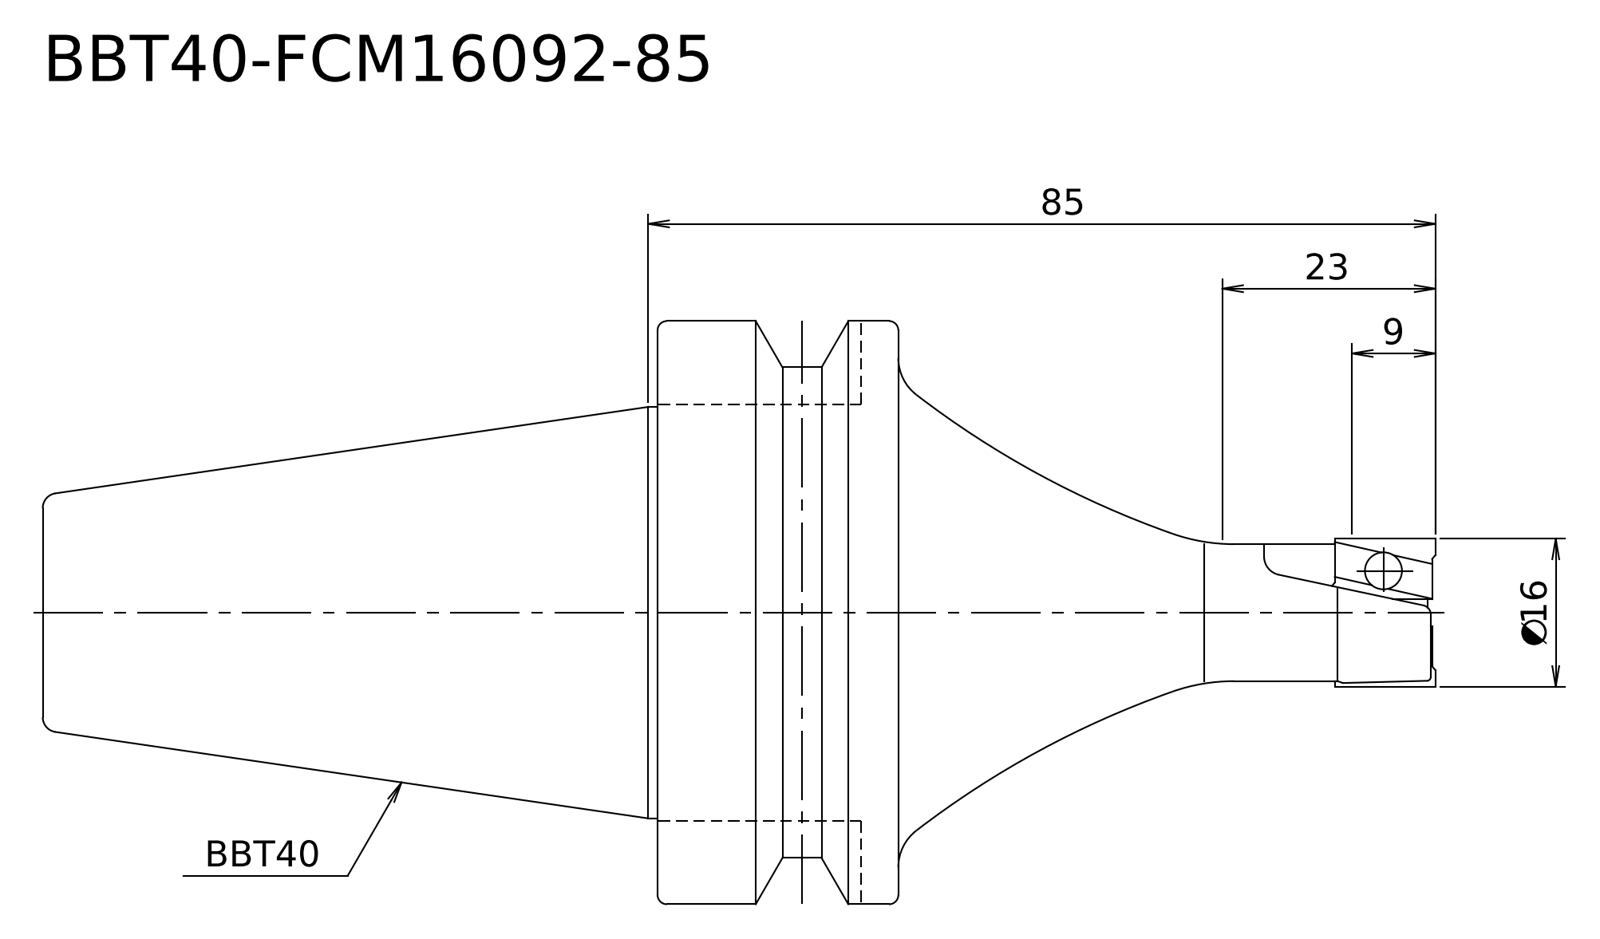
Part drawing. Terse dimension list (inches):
written by: Kubotek KeyCreator V8.5.1 (14335) (CONFIG_CONTROL_DESIGN)
unit: in
bodies: 1 solid, 17 faces (4 planar, 6 cylindrical, 7 other)
size: 5.921 × 2.48 × 2.48
volume: 10.59 in³; area: 33.55 in²
bosses: 1× ⌀2.48, 1× ⌀2.087, 1× ⌀1.75, 1× ⌀0.63, 1× ⌀0.583
face distances: 1.024, 3.638, 2.614, 2.283, 3.307, 5.921
